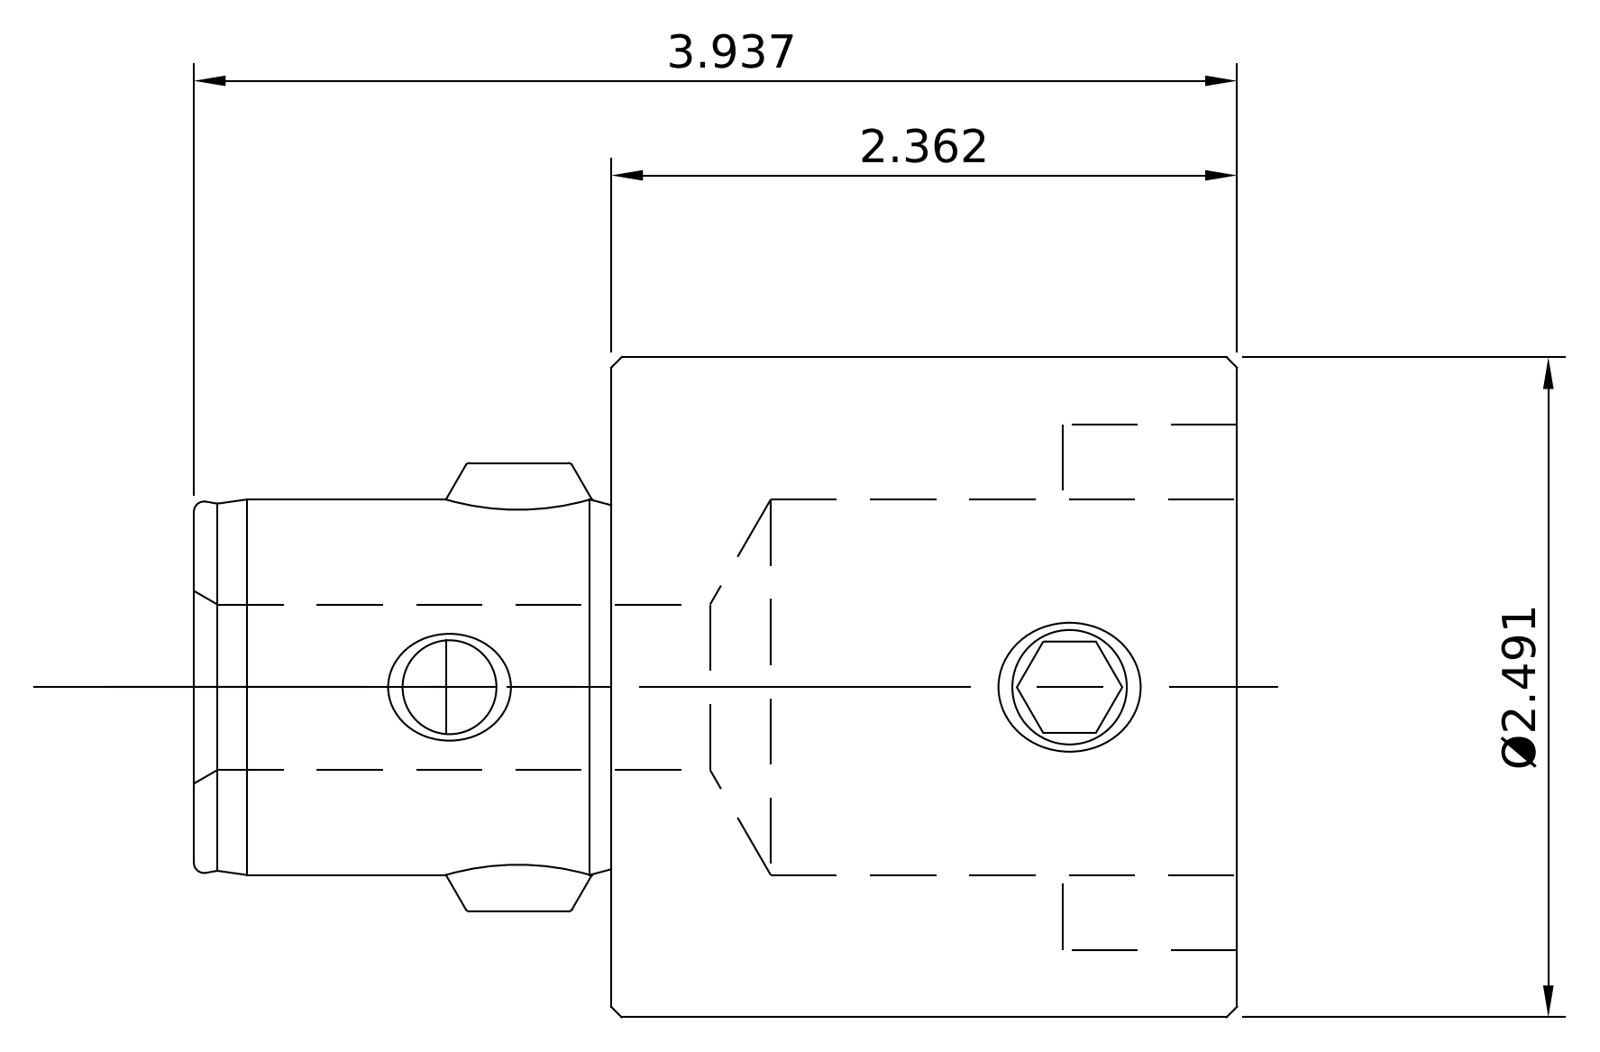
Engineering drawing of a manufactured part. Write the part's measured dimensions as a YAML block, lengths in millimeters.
part_name: "11.331.660; 10.691.50X_10.691.506; 11.331.660_11.331.660; 10.690.43X_10.690.436 (+1 more)"
step_written_by: "SolidWorks 2016 (AUTOMOTIVE_DESIGN)"
units: millimeters
bodies: {solids: 4, faces: 132, planar: 37, cylindrical: 43, other: 52}
overall_size: [100, 63.27, 63.27]
volume: 172021
surface_area: 34437
round_holes:
  - {diameter: 5, count: 1}
  - {diameter: 9, count: 1}
  - {diameter: 10.2, count: 1}
  - {diameter: 12.3, count: 1}
  - {diameter: 14, count: 1}
  - {diameter: 16, count: 1}
  - {diameter: 36, count: 1}
  - {diameter: 36.5, count: 1}
round_bosses_or_shafts:
  - {diameter: 63.27, count: 1}
  - {diameter: 62.87, count: 1}
  - {diameter: 13.9, count: 1}
  - {diameter: 12, count: 1}
  - {diameter: 11.9, count: 1}
  - {diameter: 9.9, count: 1}
partial_cylinders:
  - {radius: 5.5, count: 2}
  - {radius: 18, count: 1}
face_to_face_distances: [60, 40, 100, 30.7, 83.4, 43.4, 16.6, 43, 15.2, 27.8]
hole_center_spacings: [25, 59.45]
